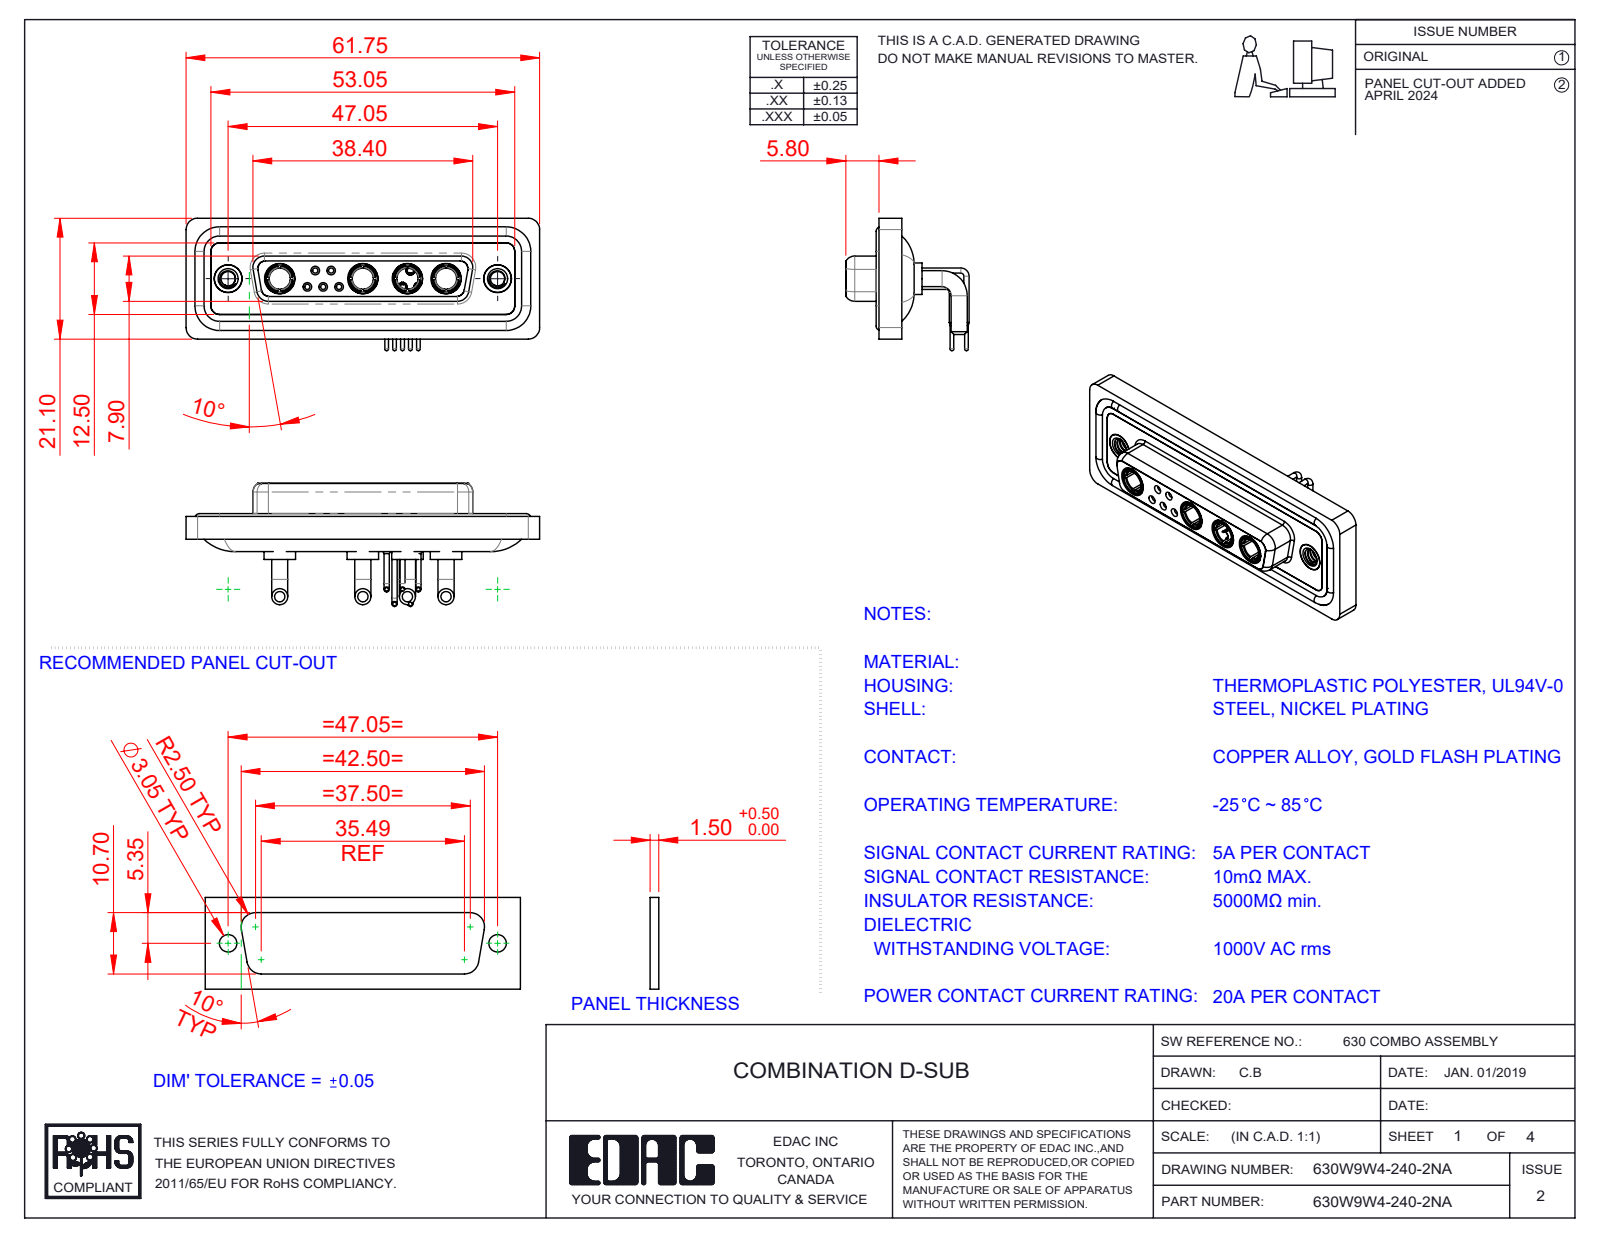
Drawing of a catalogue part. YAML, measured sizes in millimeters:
part_name: "630Combo Contact Row 2_50 Contacts; 630Combo Threaded Rivet_A; 630Combo Shell Front_25 Contacts; 630Combo Waterproof Housing_25 Contacts (+5 more)"
step_written_by: "SolidWorks 2023 (CONFIG_CONTROL_DESIGN)"
units: millimeters
bodies: {solids: 20, faces: 957, planar: 296, cylindrical: 401, other: 260}
overall_size: [61.75, 23.12, 21.53]
volume: 8444
surface_area: 14050
round_holes:
  - {diameter: 4.85, count: 6}
  - {diameter: 0.9, count: 5}
  - {diameter: 1.1, count: 5}
  - {diameter: 1.5, count: 5}
  - {diameter: 2, count: 5}
  - {diameter: 3.7, count: 4}
  - {diameter: 5.3, count: 4}
  - {diameter: 1.6, count: 3}
  - {diameter: 1.7, count: 2}
  - {diameter: 2.5, count: 2}
  - {diameter: 4, count: 2}
  - {diameter: 4.05, count: 2}
round_bosses_or_shafts:
  - {diameter: 0.9, count: 10}
  - {diameter: 1.6, count: 9}
  - {diameter: 2.8, count: 8}
  - {diameter: 2, count: 5}
  - {diameter: 1.5, count: 5}
  - {diameter: 0.65, count: 5}
  - {diameter: 5.5, count: 4}
  - {diameter: 5.2, count: 4}
partial_cylinders:
  - {radius: 1.5, count: 18}
  - {radius: 2, count: 18}
  - {radius: 1.35, count: 8}
  - {radius: 1.6, count: 8}
  - {radius: 0.25, count: 4}
  - {radius: 0.5, count: 4}
  - {radius: 0.6, count: 4}
  - {radius: 0.65, count: 4}
face_to_face_distances: [0.4, 1.8, 4.1, 1.1, 1.5, 1.6, 2.5, 3.1, 3.7, 1.4]
hole_center_spacings: [3.16, 2.77, 5.04, 13.85, 11.08, 12.79, 15.5, 5.54]
